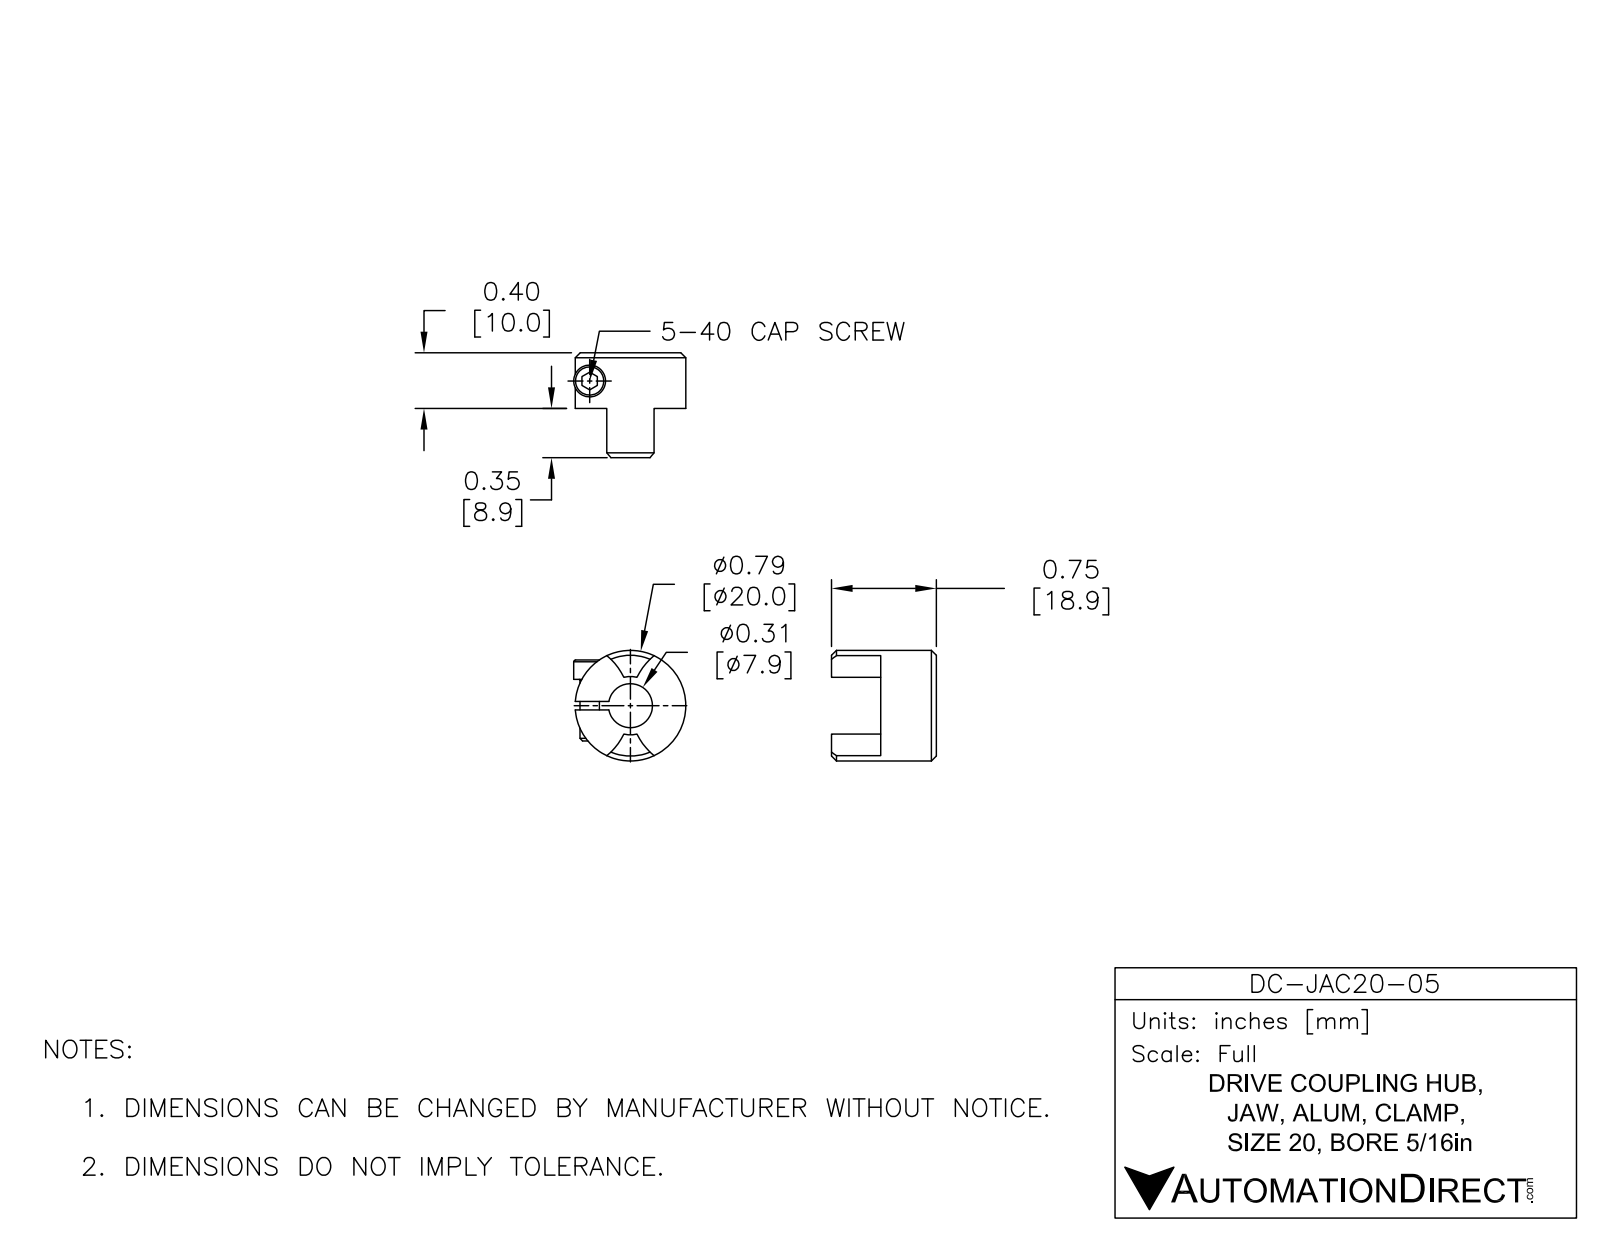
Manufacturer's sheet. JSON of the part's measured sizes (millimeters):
{"part_name": "DC-JAC20-05", "step_written_by": "SolidWorks 2015 (AUTOMOTIVE_DESIGN)", "units": "millimeters", "bodies": {"solids": 1, "faces": 23, "planar": 7, "cylindrical": 13, "other": 3}, "overall_size": [19.96, 19.93, 18.92], "volume_mm3": 2819, "surface_area_mm2": 1896, "round_holes": [[3.58, 1], [7.94, 1]], "round_bosses_or_shafts": [[19.96, 1]], "partial_cylinders_radius": [[11.68, 2], [2.78, 1], [5.26, 1]], "face_to_face_distances": [10.03, 1.52, 18.92, 8.89, 3.99, 5.51]}
